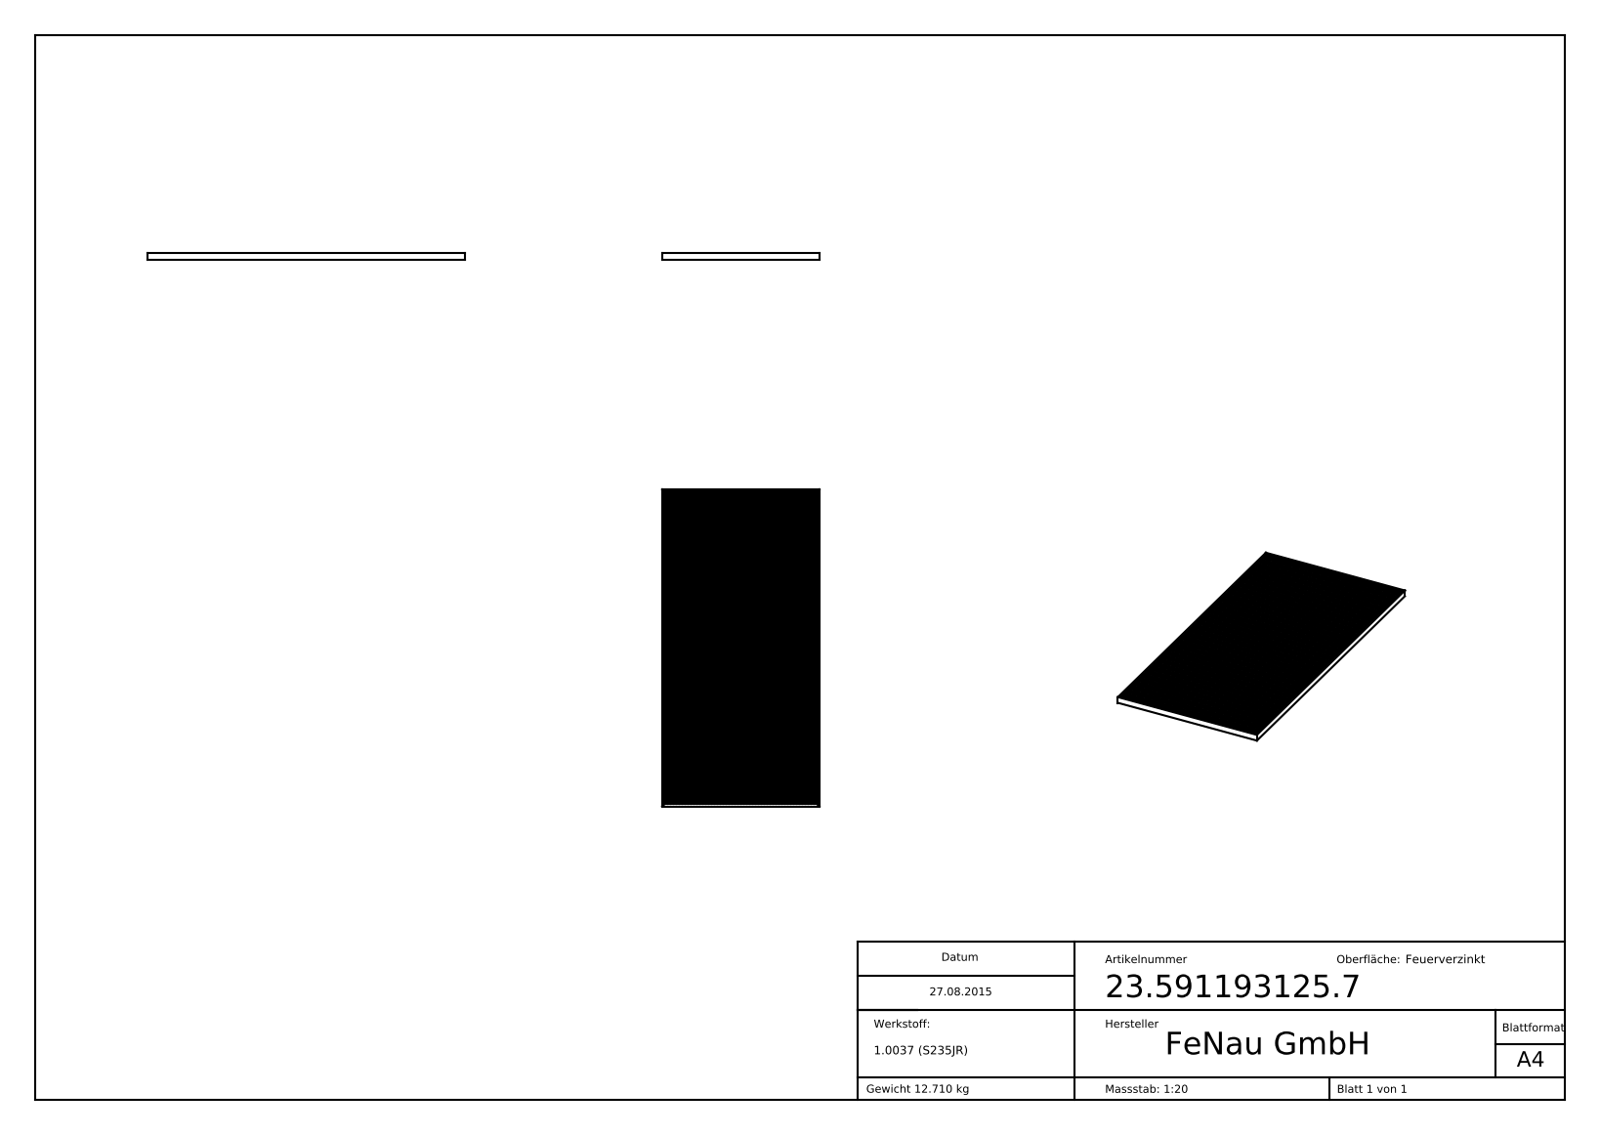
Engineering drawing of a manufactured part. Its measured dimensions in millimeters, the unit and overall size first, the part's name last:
Units: millimetres
Overall size (bounding box): 1190 × 590 × 25
Main face-to-face distances: 31.5, 63, 94.5, 126, 157.5, 11, 189, 22, 220.5, 33
Volume: 1 629 000 mm³ · Surface area: 2 651 000 mm²
Bodies: 1 solid, 6570 faces (6570 planar, 0 cylindrical, 0 other)
Part name (STEP PRODUCT): 23-591193125-7
STEP written by: SolidWorks 2015 (CONFIG_CONTROL_DESIGN)
